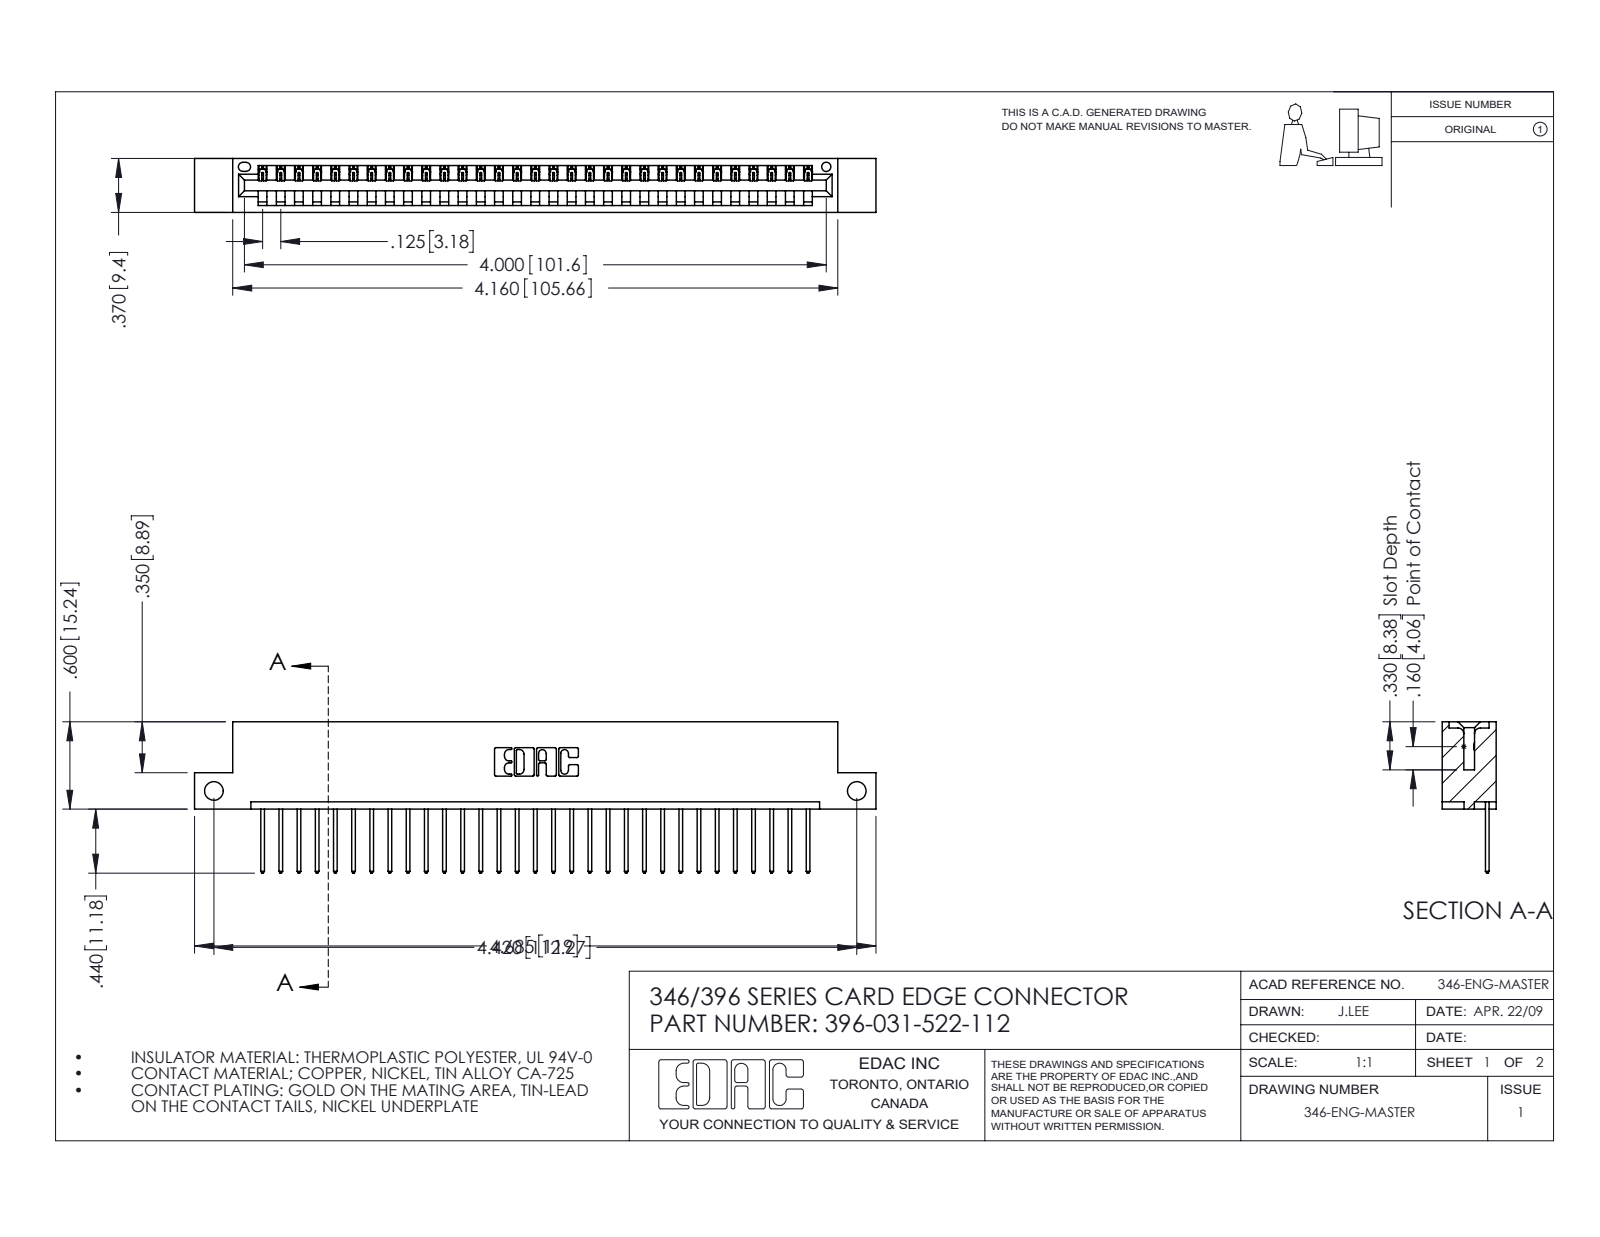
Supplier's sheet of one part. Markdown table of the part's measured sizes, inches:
| quantity | value |
| --- | --- |
| part name | 396-031-522-112; 346 Part_Flush Mounting Lugs - Side Mount; 345-292-001_345-293-122 |
| STEP written by | SolidWorks 2016 (CONFIG_CONTROL_DESIGN) |
| units | inches |
| bodies | 32 solids, 1920 faces (1316 planar, 604 cylindrical, 0 other) |
| overall size | 4.685 × 1.04 × 0.37 |
| volume | 0.685 in³ |
| surface area | 21.53 in² |
| round holes (diameter × count) | 0.128 × 2, 0.064 × 1 |
| partial cylindrical surfaces (radius × count) | 0.006 × 62, 0.01 × 62, 0.01 × 22, 0.007 × 6, 0.031 × 6, 0.026 × 3, 0.031 × 2, 0.04 × 2 |
| main face-to-face distances | 0.048, 0.322, 0.25, 0.37, 0.072, 0.298, 0.025, 0.148, 0.222, 0.1 |
| hole center spacings | 4.42 |
